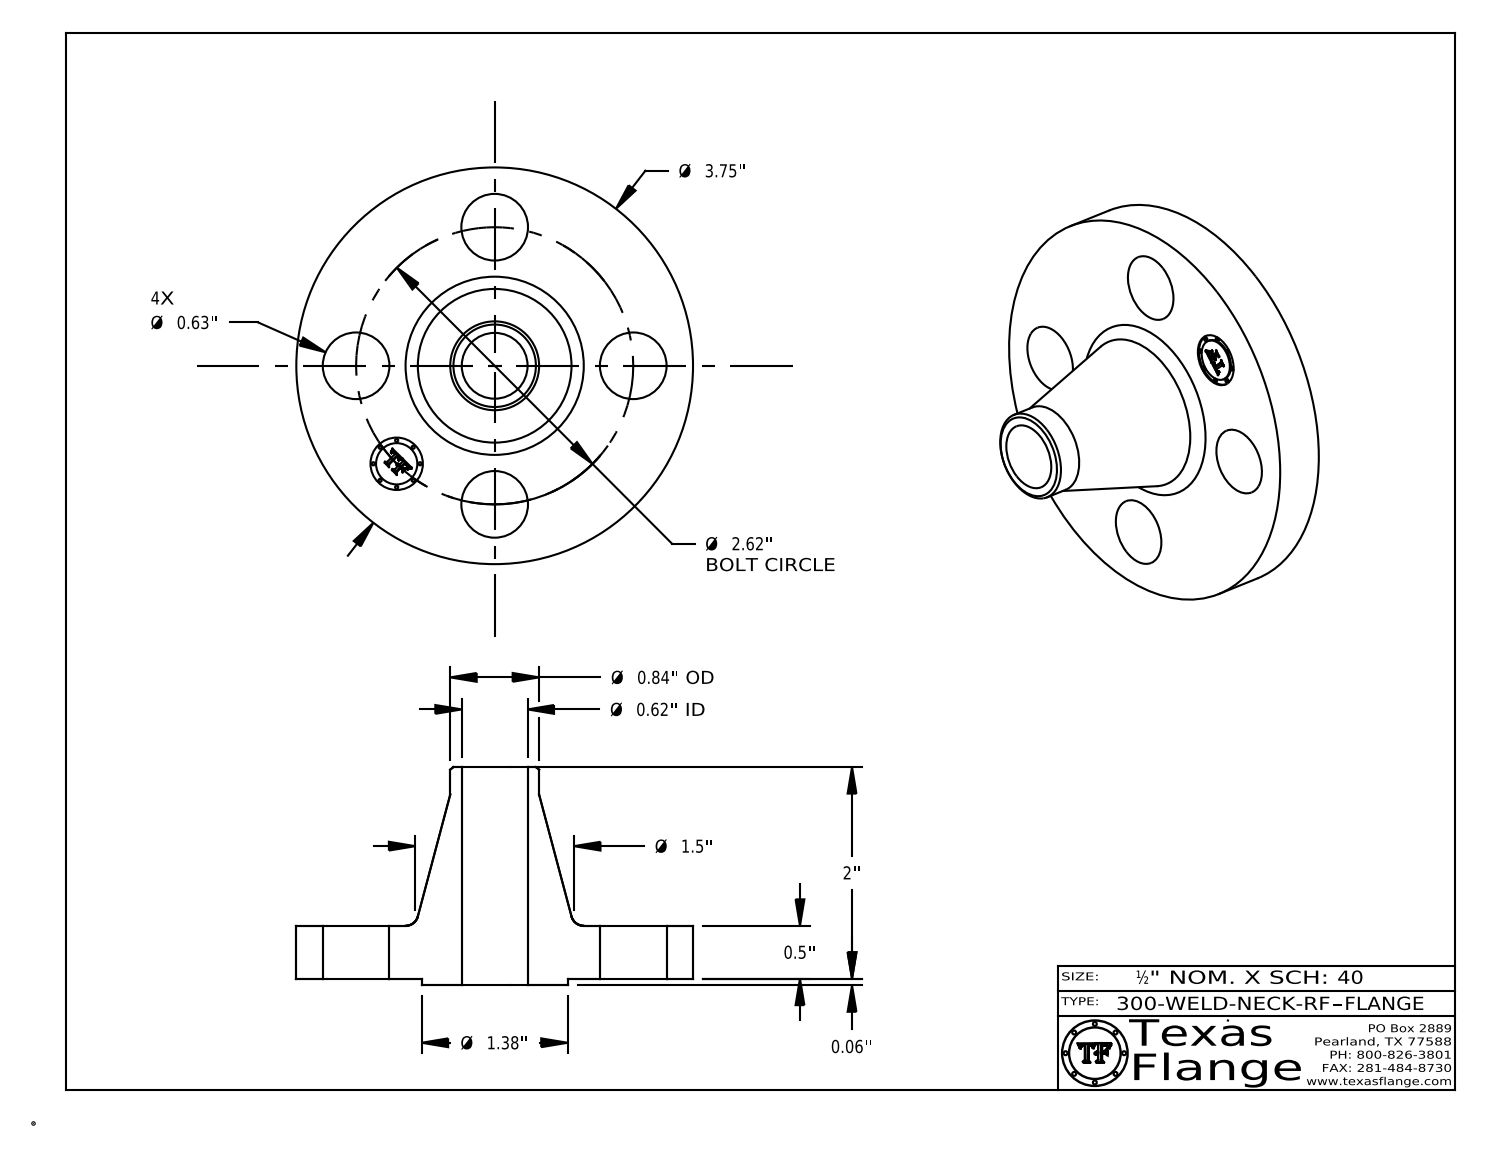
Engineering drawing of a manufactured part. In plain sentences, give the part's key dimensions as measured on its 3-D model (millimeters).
The part is named "300-WELD-NECK-RF". Its 3-D file was written by "CATIA V5 STEP AP214 (AUTOMOTIVE_DESIGN)". It is 1 solid with 411 faces: 369 planar, 36 cylindrical and 6 other. Overall it measures 95.3 by 95.3 by 52.4 millimeters. Its volume is 96 420 cubic millimeters and its surface area 24 040 square millimeters. Round holes: 4 of diameter 16, 1 of diameter 12.6, 1 of diameter 15.8. Round bosses or shafts: 8 of diameter 0.8, 1 of diameter 95.3, 1 of diameter 35.1, 1 of diameter 21.3, 1 of diameter 9.9. The main face-to-face distances are 12.7, 1.6, 14.3, 52.4, 50.8, 38.1, 13.9, 12.3, 0.4, 38.5. The hole center spacings are 33.3, 47, 25.5, 61.5, 66.5, 33.3.
